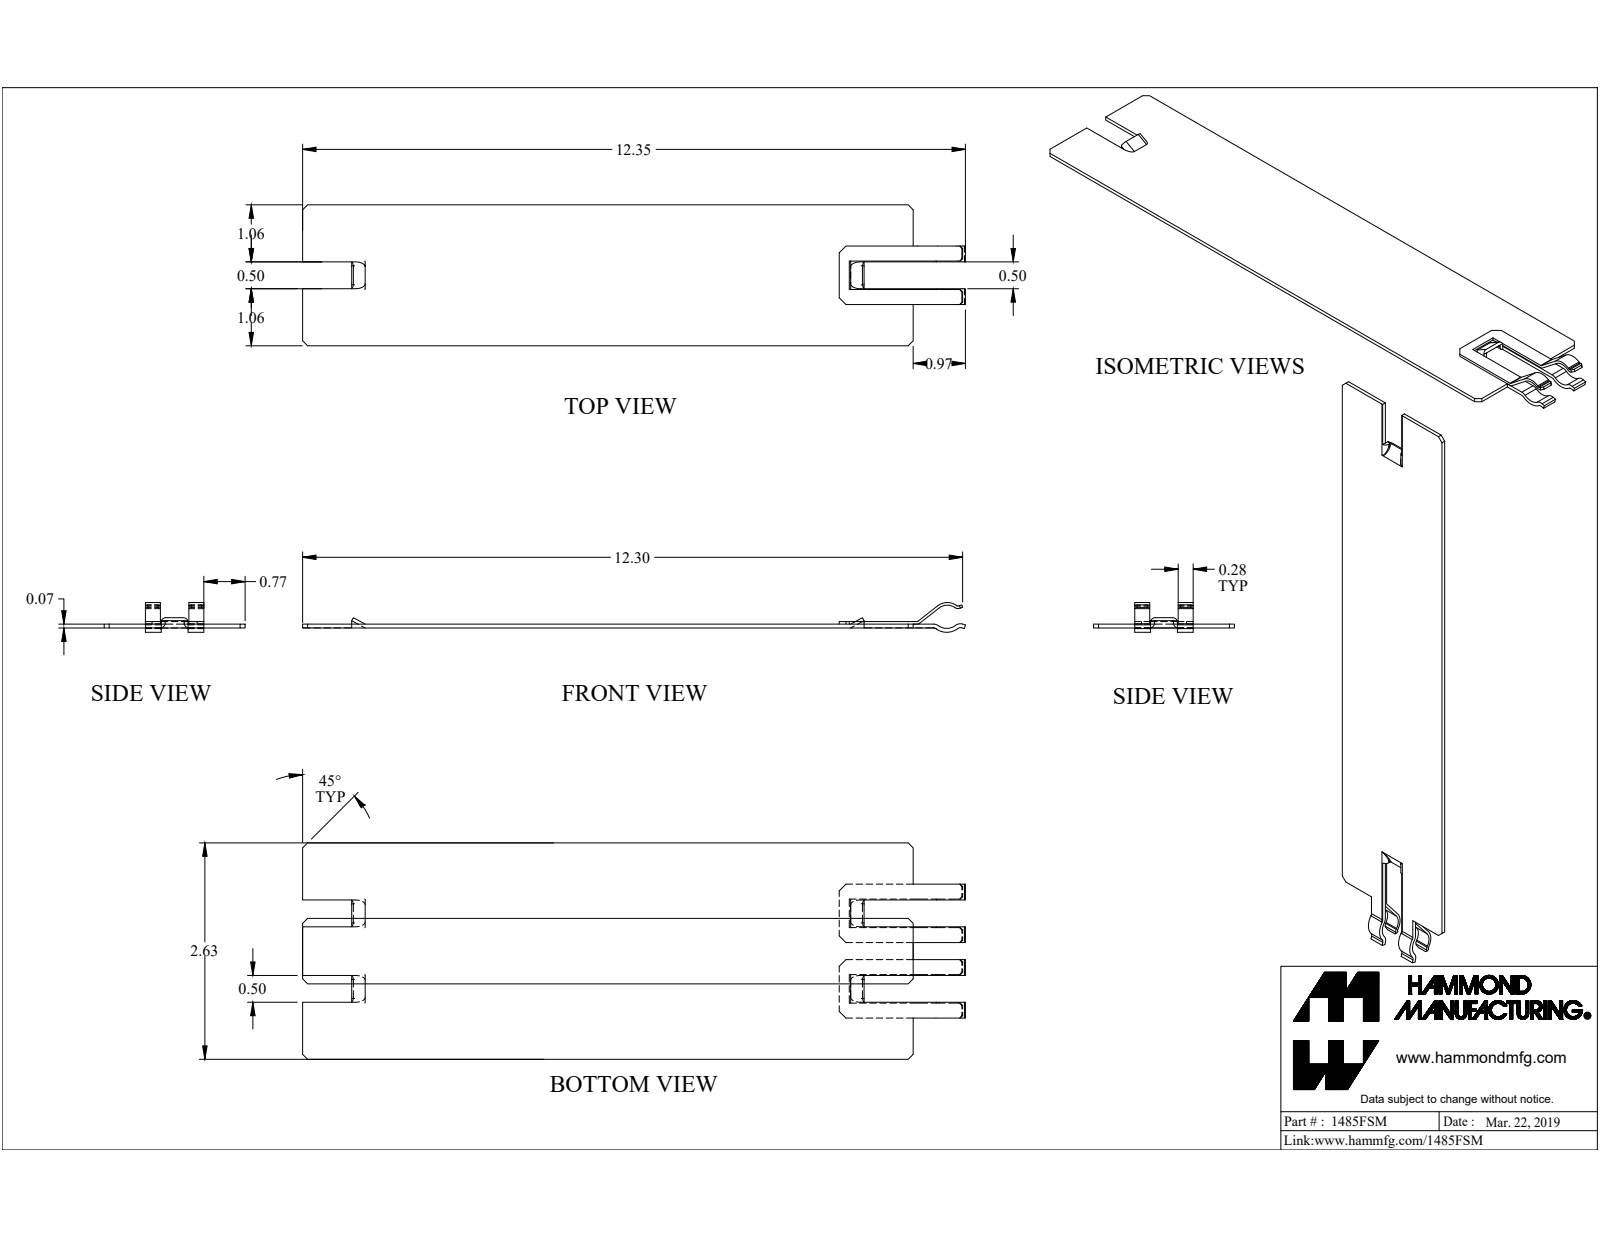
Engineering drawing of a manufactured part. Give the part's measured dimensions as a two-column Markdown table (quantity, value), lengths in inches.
| quantity | value |
| --- | --- |
| part name | 1485FSM |
| STEP written by | SolidWorks 2019 (CONFIG_CONTROL_DESIGN) |
| units | inches |
| bodies | 4 solids, 125 faces (83 planar, 36 cylindrical, 6 other) |
| overall size | 12.348 × 2.625 × 0.599 |
| volume | 2.687 in³ |
| surface area | 74.66 in² |
| partial cylindrical surfaces (radius × count) | 0.09 × 6, 0.015 × 4, 0.072 × 3, 0.144 × 2, 0.024 × 1, 0.03 × 1, 0.078 × 1, 0.245 × 1 |
| main face-to-face distances | 0.072, 0.125, 0.197, 0.048, 2.625, 0.245, 0.12, 0.75, 9.169, 1.063 |
